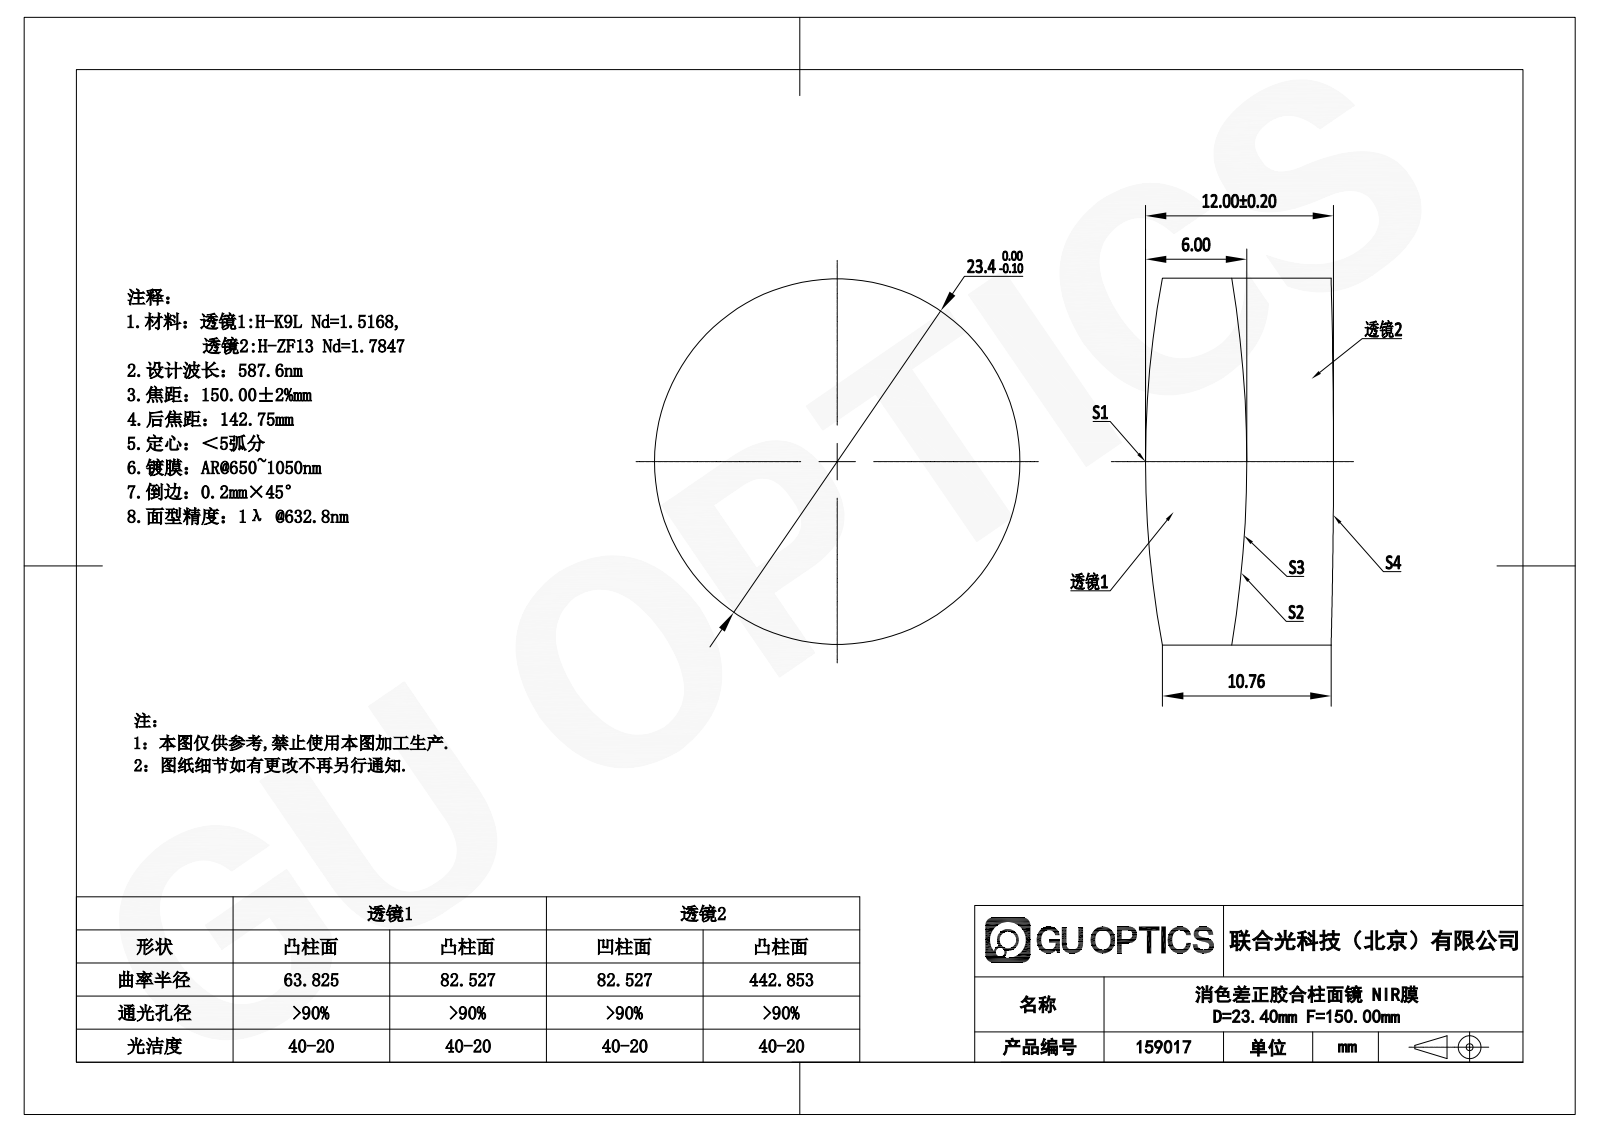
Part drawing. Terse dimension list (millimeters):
name: 159017
written by: SolidWorks 2020 (CONFIG_CONTROL_DESIGN)
unit: mm
bodies: 1 solid, 5 faces (0 planar, 5 cylindrical, 0 other)
size: 23.4 × 23.4 × 12
volume: 5 028 mm³; area: 1 699 mm²
bosses: 1× ⌀23.4
rounds: 1× R63.83, 1× R442.85
